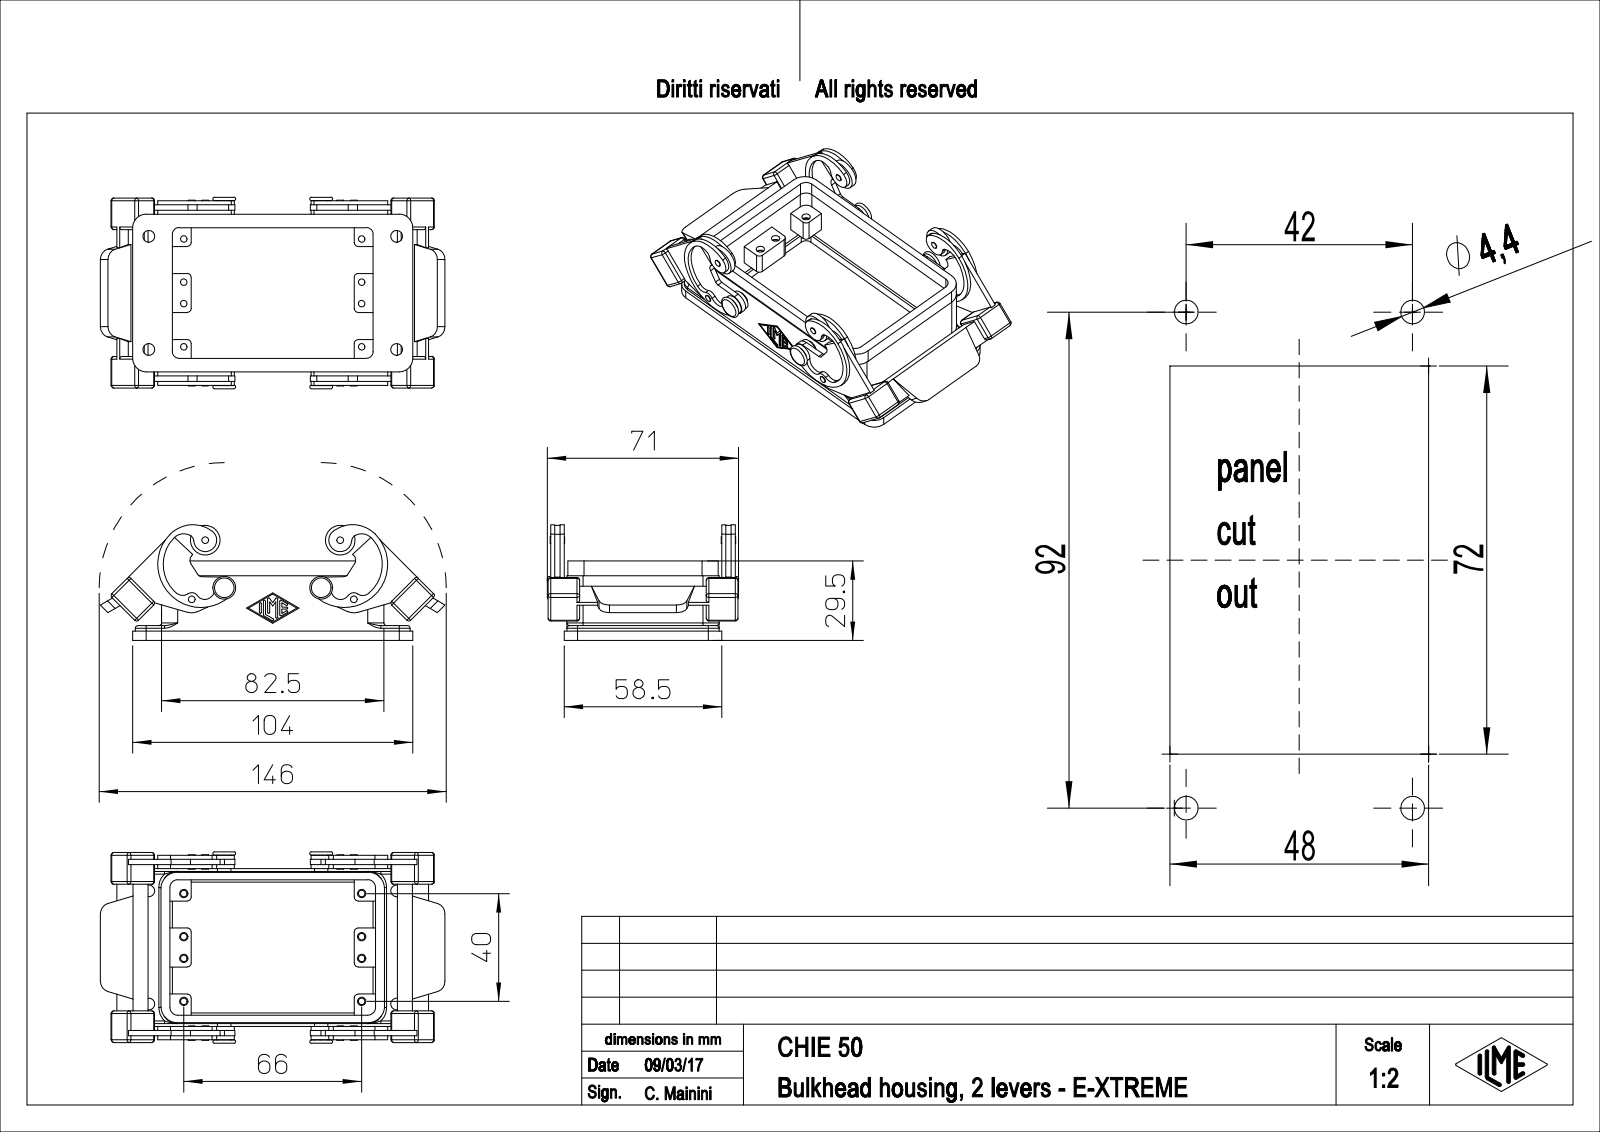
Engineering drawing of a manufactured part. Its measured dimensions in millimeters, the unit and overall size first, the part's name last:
Units: millimetres
Overall size (bounding box): 127.92 × 71 × 42.94
Round holes (diameter × count): ⌀2.46 ×8, ⌀3.1 ×8, ⌀4.4 ×4
Round bosses / shafts (diameter × count): ⌀2.5 ×4, ⌀11 ×2, ⌀5 ×2
Partial cylindrical surfaces — rounded edges, fillets, slot ends (radius × count): R1 ×46, R0.38 ×14, R1.5 ×10, R2.5 ×10, R4 ×10, R5 ×8, R6 ×8, R2.9 ×4
Main face-to-face distances: 3, 5.5, 3.5, 63.5, 53.5, 1.5, 1, 4.5, 4, 2
Hole centre spacings: 13.04, 16, 21.4, 24, 28.18, 43.01, 66, 67.91
Volume: 55 120 mm³ · Surface area: 38 005 mm²
Bodies: 1 solid, 636 faces (266 planar, 310 cylindrical, 60 other)
Part name (STEP PRODUCT): CHIE_50
STEP written by: PTC Creo Elements/Direct Modeling 19.0E 27-Jun-2016 (C) Parametric Technology GmbH (AUTOMOTIVE_DESIGN)
